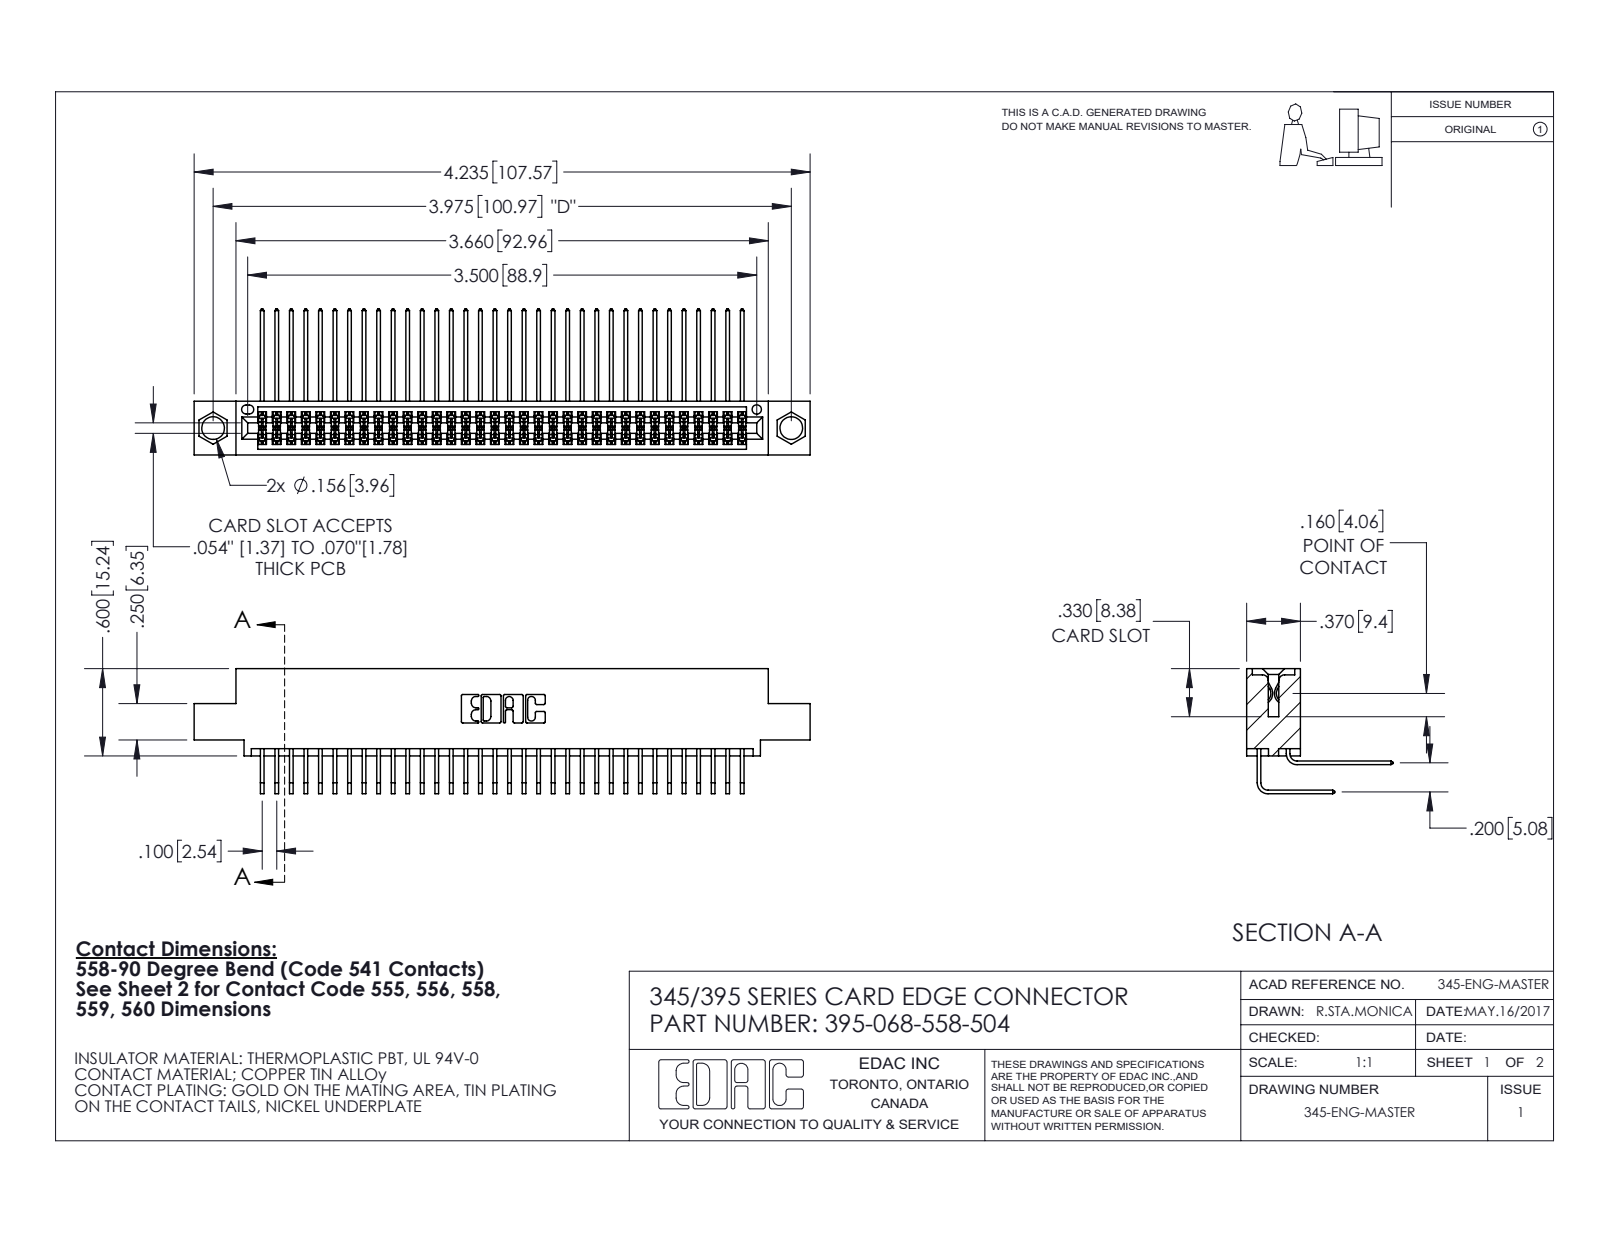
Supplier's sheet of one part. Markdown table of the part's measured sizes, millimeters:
| quantity | value |
| --- | --- |
| part name | 345-292-001_558 559 Tail - 1; 395-068-558-504; 345 Part_0.110 Offset - 0.156 Dia-TI; 345-292-001_558 Tail - 2 |
| STEP written by | SolidWorks 2020 (CONFIG_CONTROL_DESIGN) |
| units | millimeters |
| bodies | 69 solids, 3680 faces (2478 planar, 1202 cylindrical, 0 other) |
| overall size | 107.6 × 25.5 × 21.8 |
| volume | 10 600 mm³ |
| surface area | 17 280 mm² |
| round holes (diameter × count) | 4 × 2, 1.6 × 1 |
| partial cylindrical surfaces (radius × count) | 0.2 × 102, 0.3 × 22, 0.2 × 6, 0.8 × 6, 0.7 × 3, 0.4 × 2, 0.5 × 2, 0.6 × 2 |
| main face-to-face distances | 1.8, 7.6, 5.1, 9.4, 2.5, 6.9, 0.6, 5.7, 0.6, 4.4 |
| hole center spacings | 6.9, 95, 101 |
